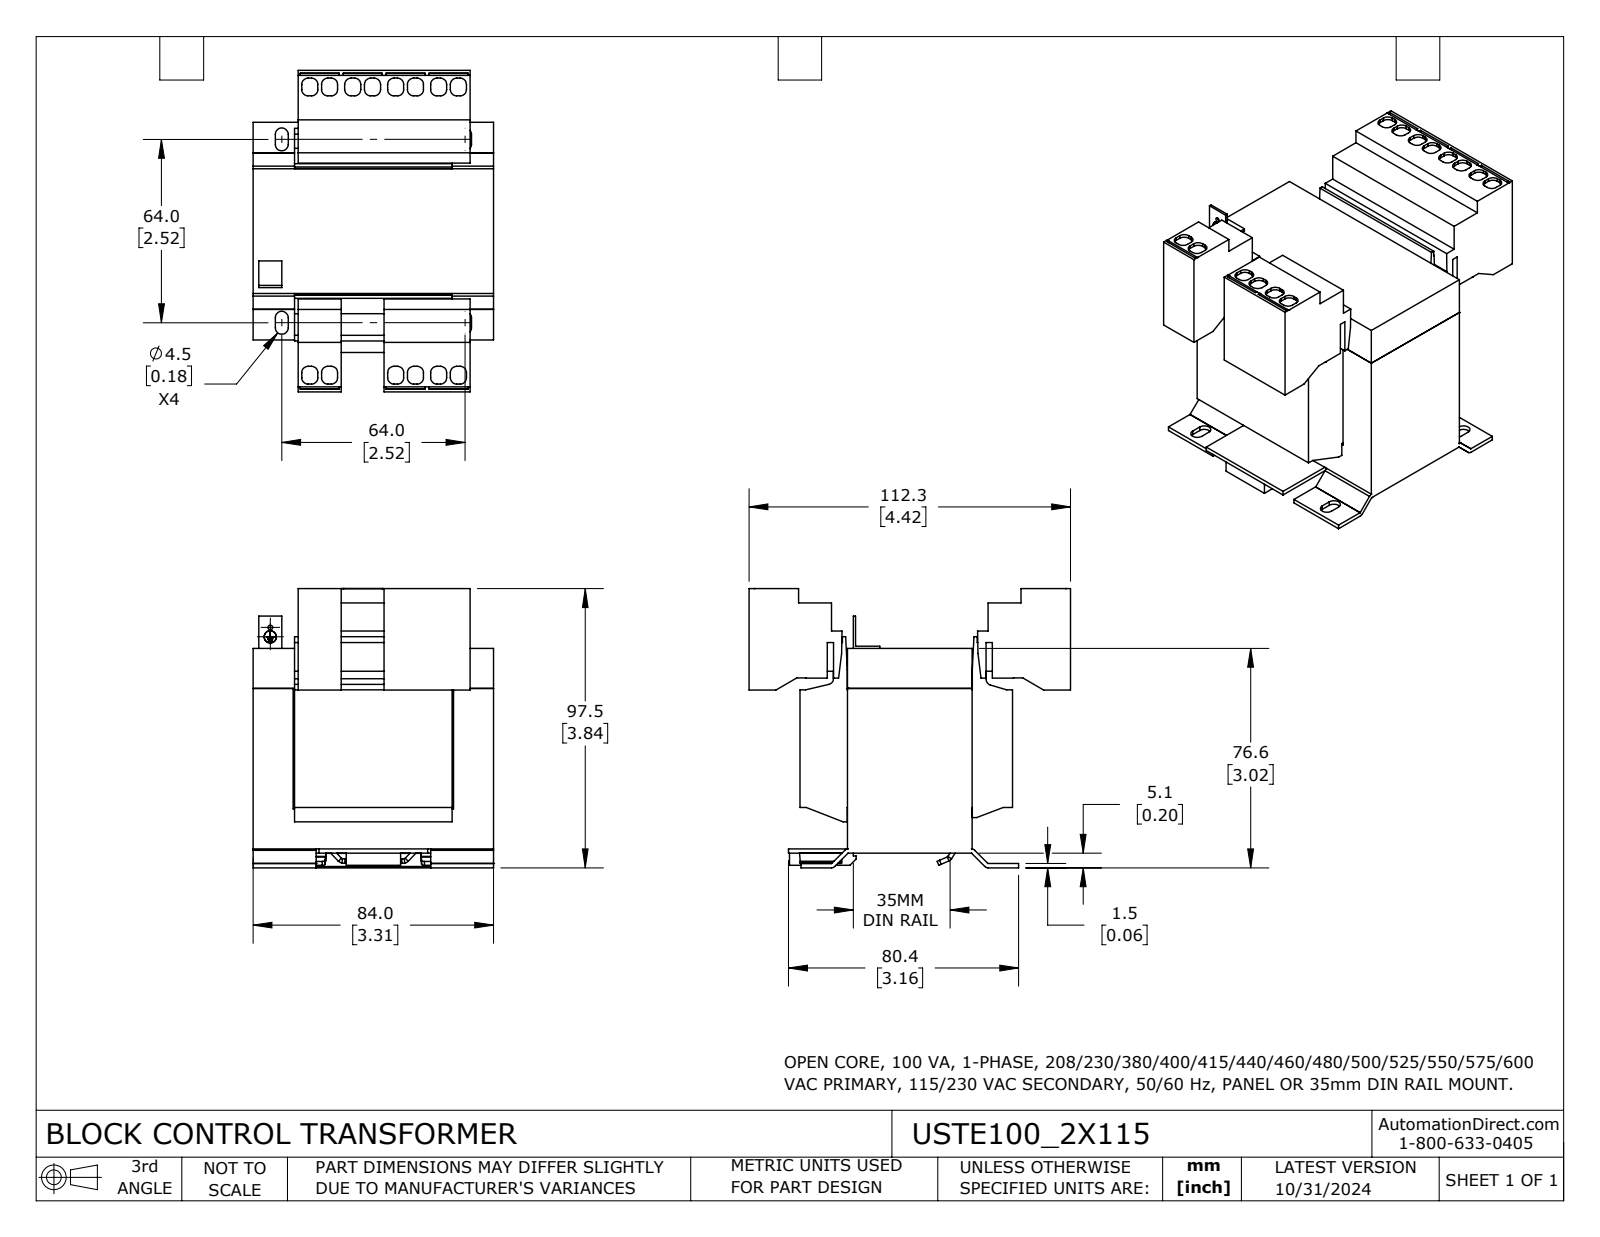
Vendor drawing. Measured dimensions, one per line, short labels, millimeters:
name: USTE100_2X115
written by: SolidWorks 2023 (CONFIG_CONTROL_DESIGN)
unit: mm
bodies: 1 solid, 555 faces (437 planar, 106 cylindrical, 12 other)
size: 112.3 × 97.5 × 84
volume: 426 400 mm³; area: 86 450 mm²
holes: 1× ⌀1.7, 1× ⌀4.3
bosses: 1× ⌀4.2
rounds: 56× R2.2, 9× R2, 8× R2.3, 4× R0.1, 4× R1, 4× R1.6, 3× R0.5
face distances: 14, 14.5, 69.5, 70, 1, 76.9, 0.5, 56, 84, 34.4
hole spacings: 3.3
